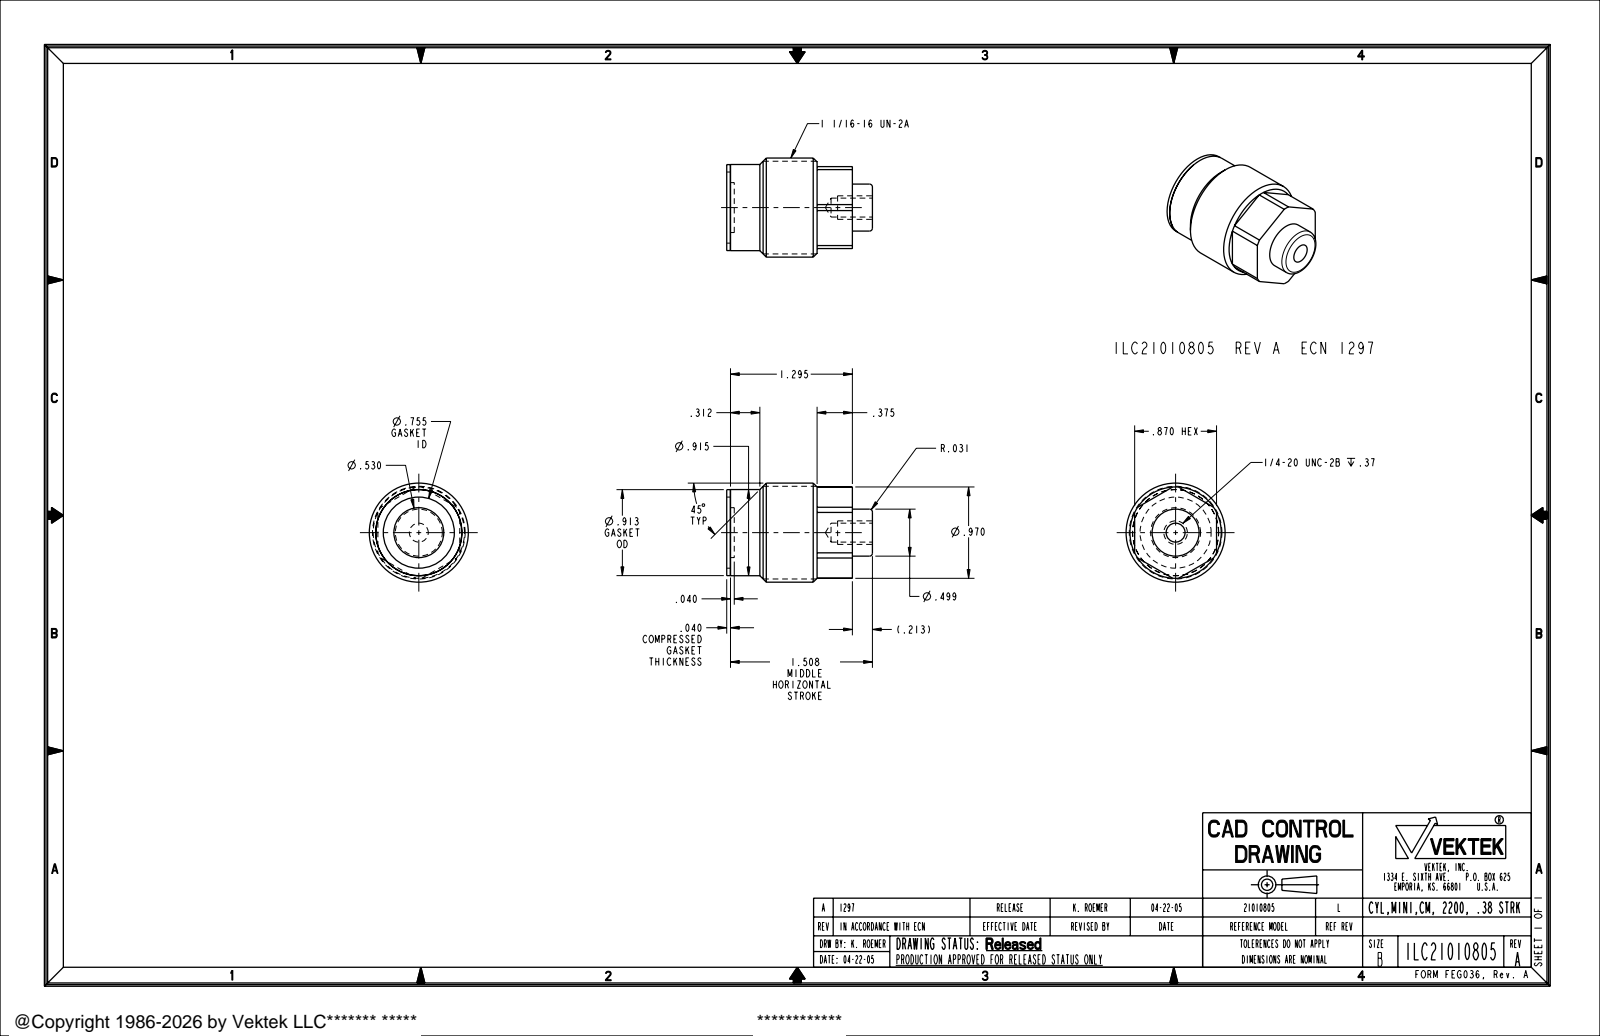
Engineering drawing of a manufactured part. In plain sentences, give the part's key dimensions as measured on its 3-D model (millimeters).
The part is named "ILC21010805". Its 3-D file was written by "PRO/ENGINEER BY PARAMETRIC TECHNOLOGY CORPORATION, 2004290 (AUTOMOTIVE_DESIGN_CC2)". It is 2 solids with 52 faces: 20 planar, 24 cylindrical and 8 other. Overall it measures 39.3 by 26.7 by 26.7 millimeters. Its volume is 16 300 cubic millimeters and its surface area 6 229 square millimeters. Round holes: 1 of diameter 5.1, 1 of diameter 13.5, 1 of diameter 19.2. Round bosses or shafts: 1 of diameter 26.7, 1 of diameter 25, 1 of diameter 23.2, 1 of diameter 23.2, 1 of diameter 12.7, 1 of diameter 6.4. Partial cylindrical surfaces (rounded edges, fillets, slot ends): 1 of radius 12.3. The main face-to-face distances are 22.1, 9.5, 23.4, 32.9, 1, 22.4, 31.9, 1, 2, 24.4.
